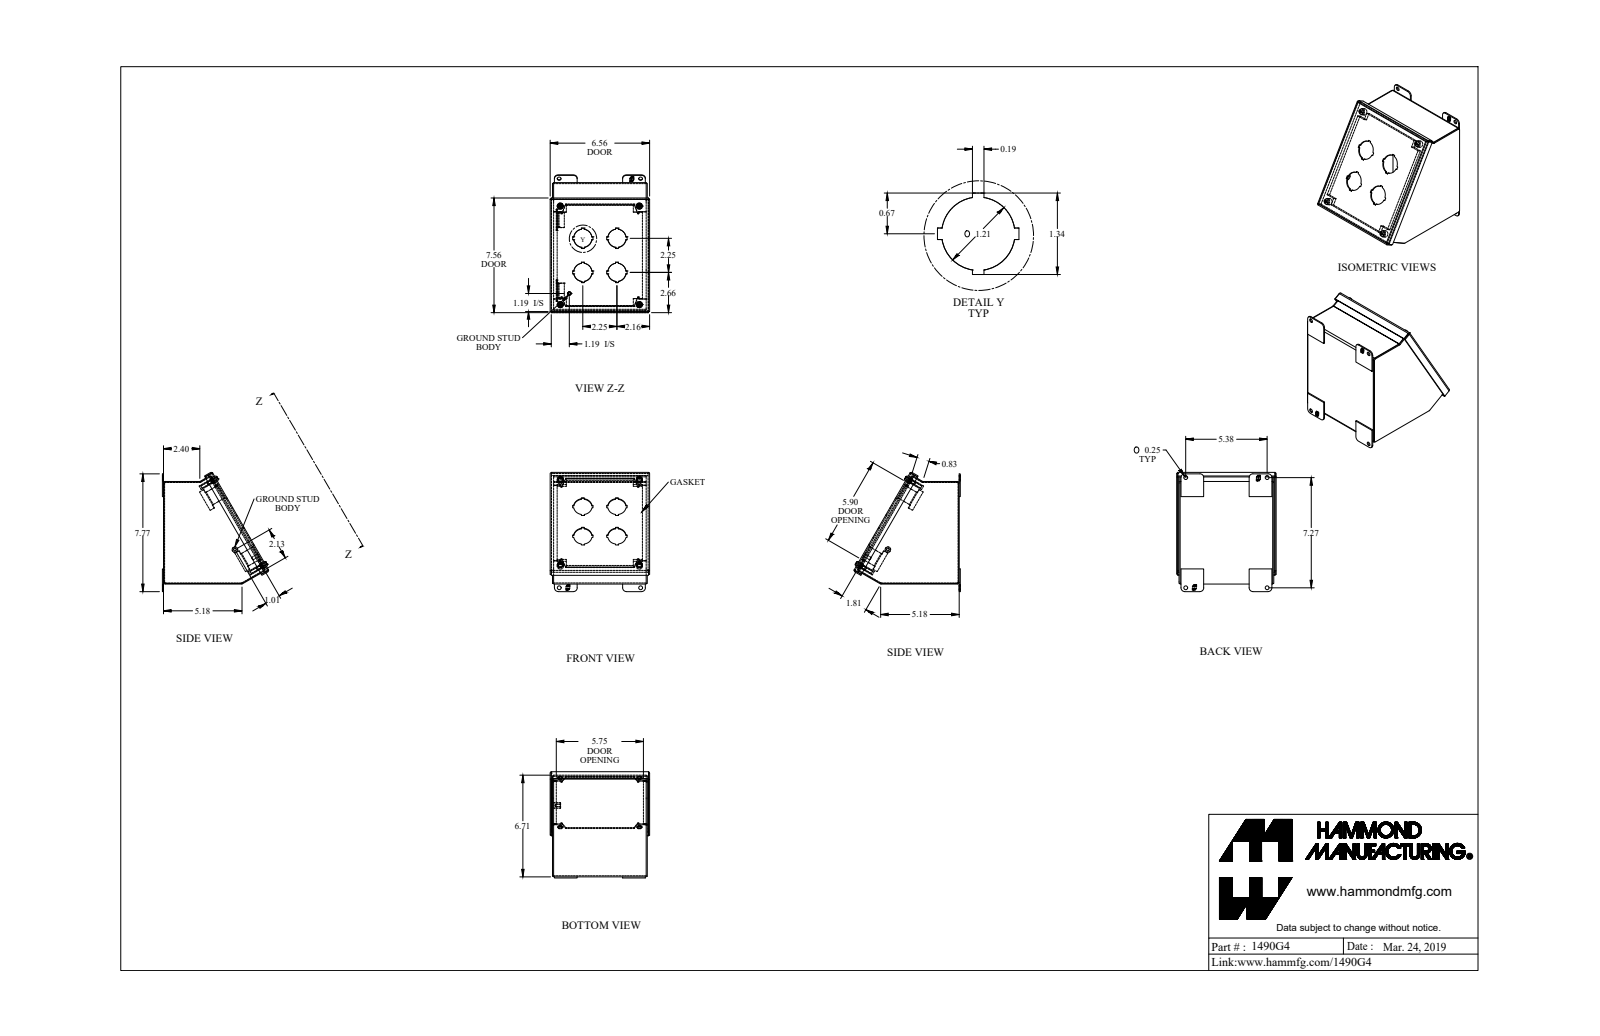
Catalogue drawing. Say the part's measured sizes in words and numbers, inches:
The part is named "1490G4_Default". Its 3-D file was written by "SolidWorks 2019 (CONFIG_CONTROL_DESIGN)". It is 25 solids with 775 faces: 547 planar, 188 cylindrical and 40 other. Overall it measures 7.869 by 7.008 by 6.562 inches. Its volume is 20.56 cubic inches and its surface area 552.3 square inches. Round holes: 8 of diameter 0.25, 4 of diameter 0.159, 4 of diameter 0.406, 4 of diameter 1.21, 1 of diameter 0.156. Round bosses or shafts: 4 of diameter 0.39, 4 of diameter 0.19, 4 of diameter 0.148, 2 of diameter 0.275, 2 of diameter 0.275, 1 of diameter 0.375, 1 of diameter 0.25, 1 of diameter 0.188. Partial cylindrical surfaces (rounded edges, fillets, slot ends): 18 of radius 0.108, 12 of radius 0.036, 8 of radius 0.25, 6 of radius 0.029, 6 of radius 0.086, 4 of radius 0.125, 4 of radius 0.16, 4 of radius 0.171. The main face-to-face distances are 0.072, 6.178, 6.106, 6.25, 6.697, 6.769, 6.625, 0.156, 6.334, 0.072. The hole center spacings are 6.5, 8.33, 5.21, 5.215, 5.224, 4.293, 4.298, 8.339.
